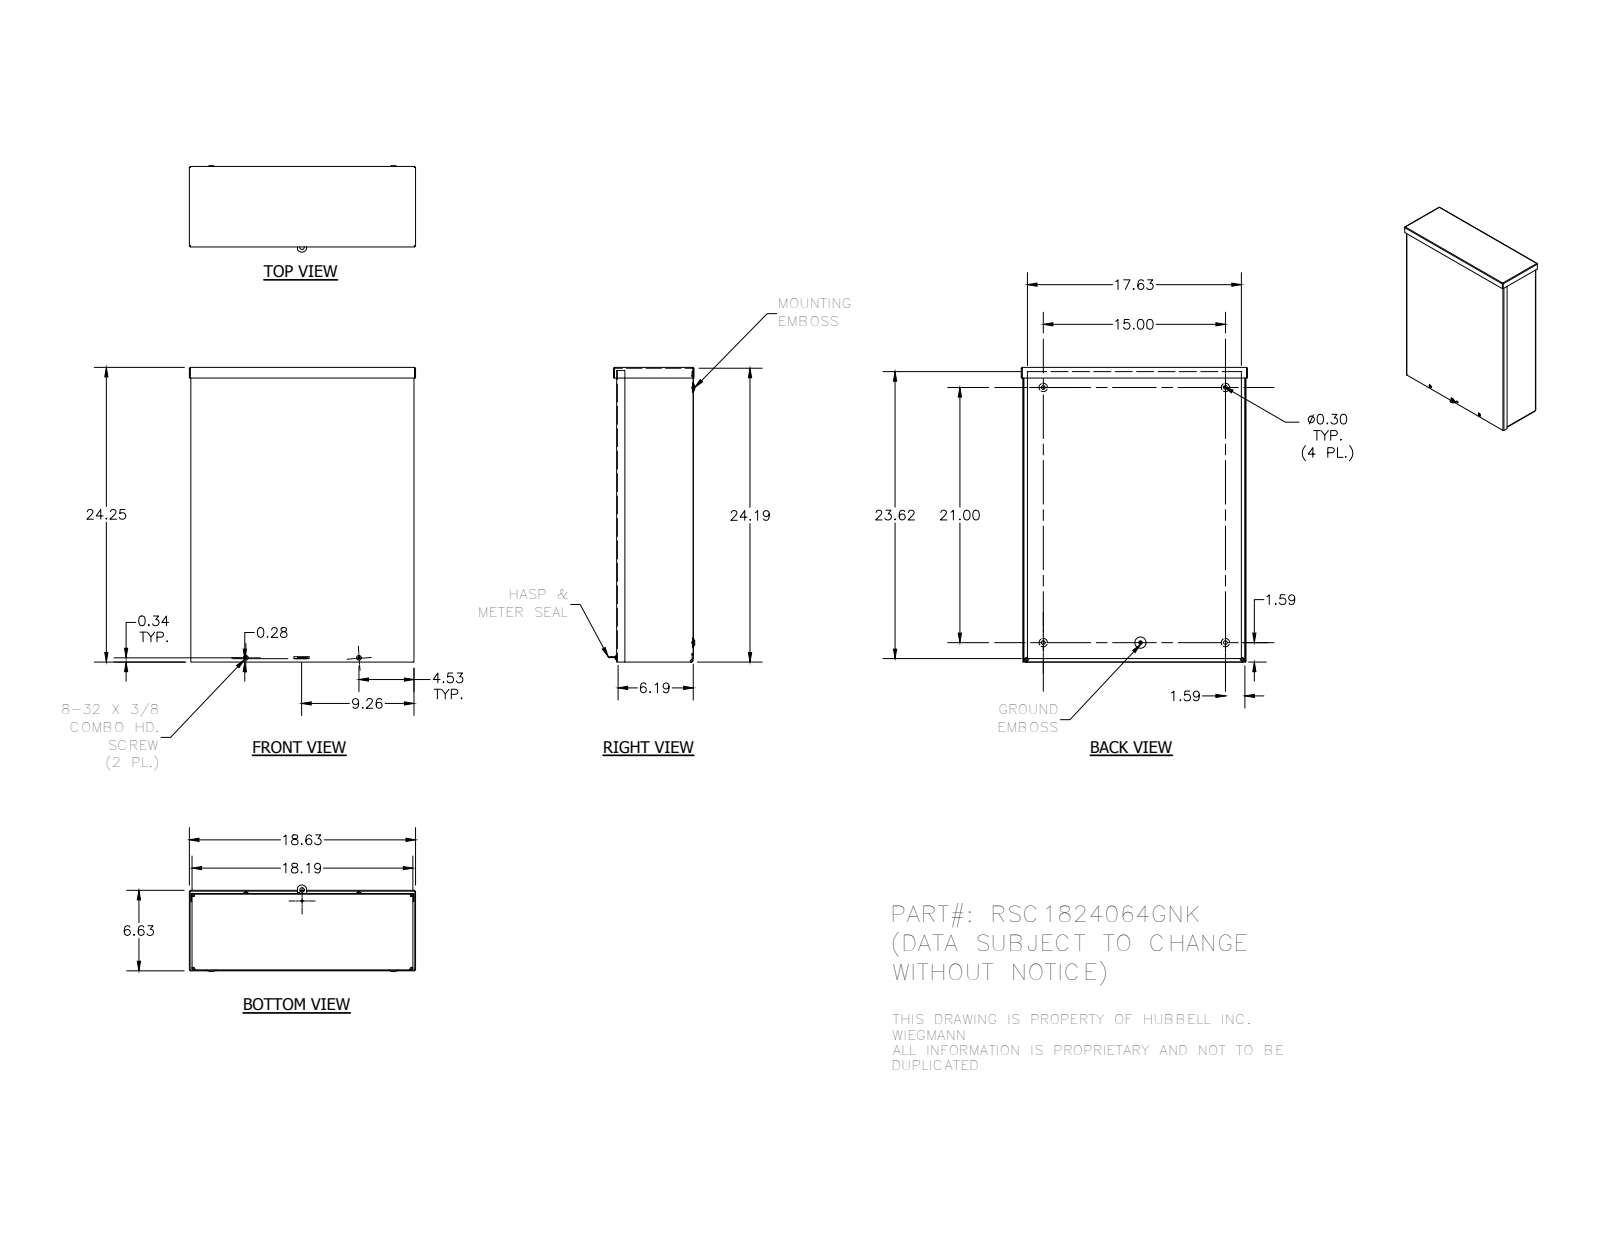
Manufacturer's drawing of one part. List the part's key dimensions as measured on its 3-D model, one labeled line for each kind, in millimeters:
Part name (STEP PRODUCT): RSC182406GNK_WRAP; RSC1824GNK_LID; RSC1806GNK_CAP; 3183 (+3 more)
STEP written by: Autodesk Inventor 2014 (AUTOMOTIVE_DESIGN)
Units: millimetres
Bodies: 7 solids, 377 faces (163 planar, 78 cylindrical, 136 other)
Overall size (bounding box): 615.96 × 473.07 × 180.97
Volume: 1 723 000 mm³ · Surface area: 2 202 000 mm²
Round holes (diameter × count): ⌀7.62 ×4, ⌀7.95 ×4, ⌀3.17 ×2, ⌀3.76 ×2, ⌀3.96 ×1, ⌀4.19 ×1, ⌀9.52 ×1
Round bosses / shafts (diameter × count): ⌀9.75 ×2, ⌀4.17 ×2, ⌀5.8 ×1
Partial cylindrical surfaces — rounded edges, fillets, slot ends (radius × count): R0.79 ×8, R2.37 ×8, R3.17 ×8, R4.75 ×8, R1.4 ×4, R1.57 ×4, R2.38 ×4, R2.97 ×4
Main face-to-face distances: 1.58, 158.73, 157.15, 1.59, 160.32, 158.74, 1.57, 460.39, 612.79, 3.15
Hole centre spacings: 236.55, 381, 533.4, 569.78, 592.13, 637.63, 639.79, 655.5
